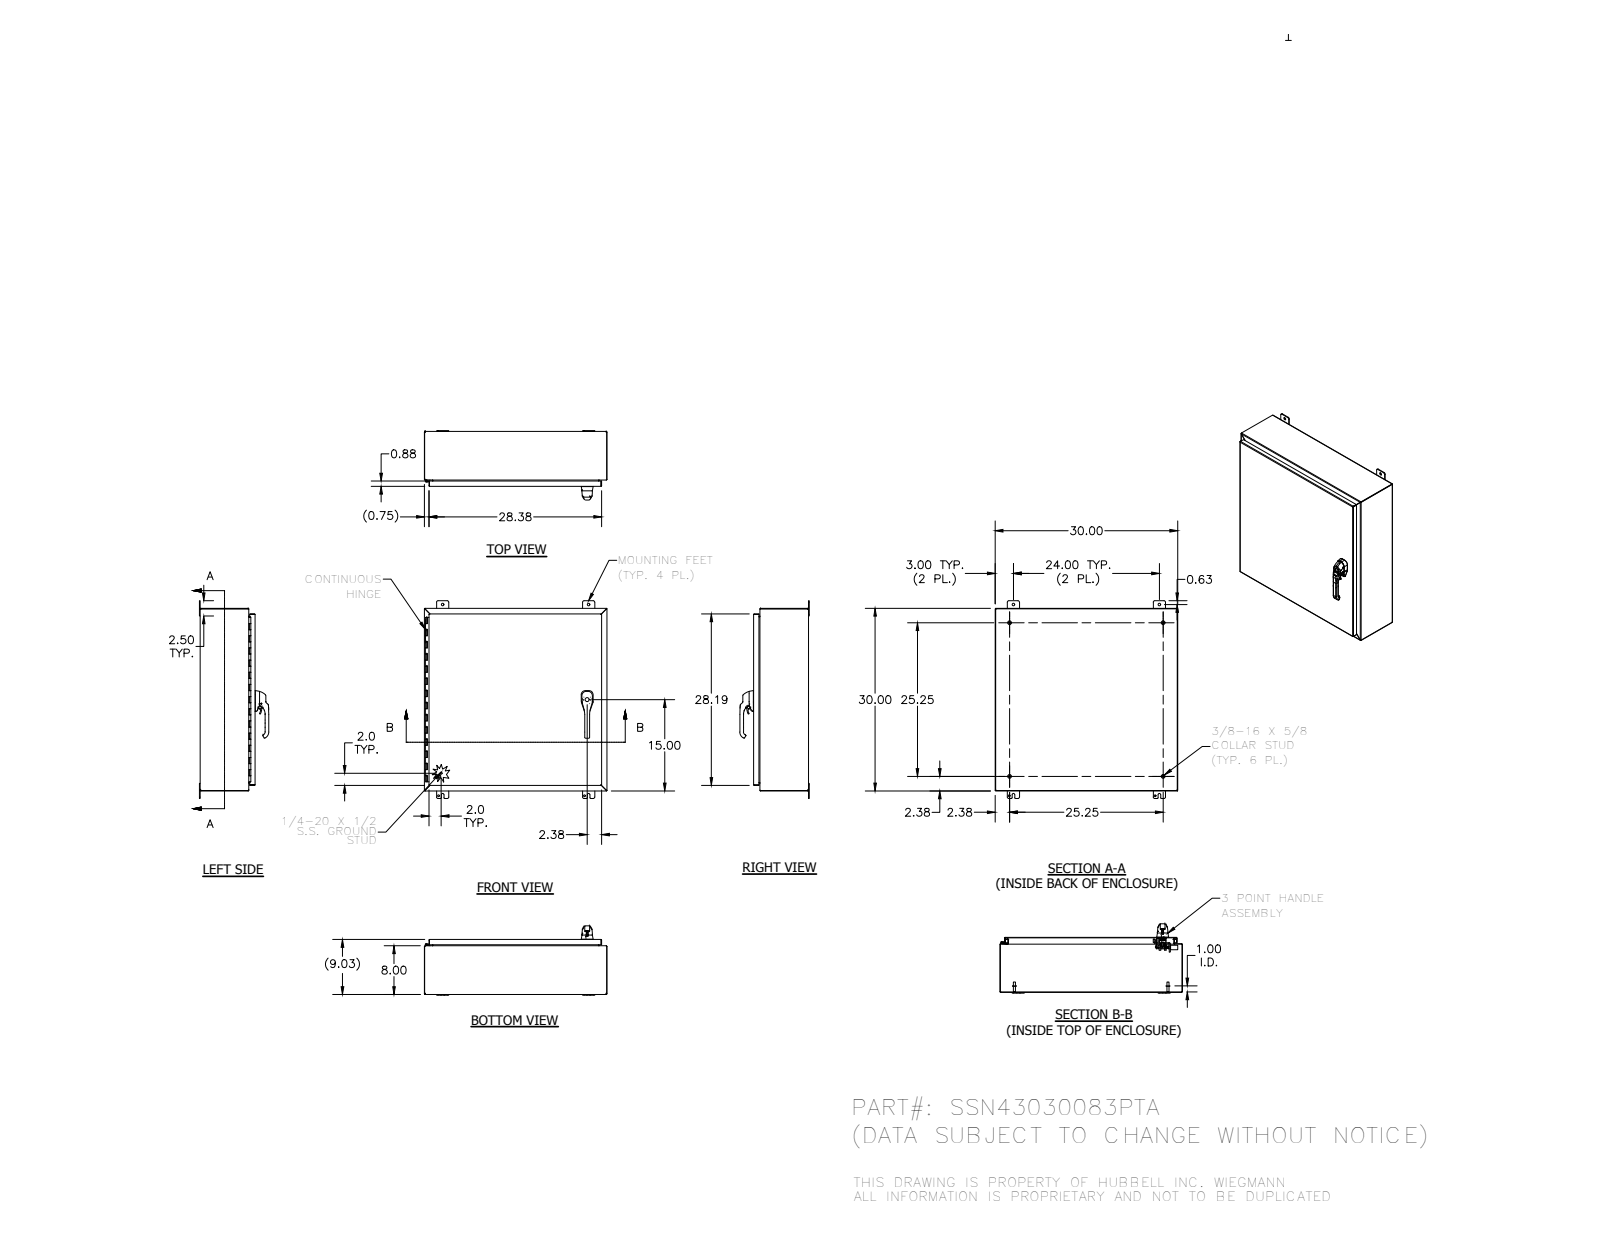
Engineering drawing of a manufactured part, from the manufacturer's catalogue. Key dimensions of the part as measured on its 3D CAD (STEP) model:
Part name (STEP PRODUCT): HFW32451; 1091-903_AF0; HFW3762; SSN43030083PTABKP (+8 more)
STEP written by: SolidWorks 2014 (AUTOMOTIVE_DESIGN)
Units: inches
Bodies: 56 solids, 3140 faces (1047 planar, 1306 cylindrical, 787 other)
Overall size (bounding box): 32.5 × 30 × 11.408
Volume: 254 in³ · Surface area: 6 591 in²
Round holes (diameter × count): ⌀0.262 ×8, ⌀0.187 ×4, ⌀0.313 ×4, ⌀0.438 ×4, ⌀0.213 ×3, ⌀0.281 ×3, ⌀0.241 ×2, ⌀0.25 ×2, ⌀0.252 ×2, ⌀0.315 ×2, ⌀0.4 ×2, ⌀0.402 ×2
Round bosses / shafts (diameter × count): ⌀0.625 ×4, ⌀0.33 ×4, ⌀0.236 ×3, ⌀1 ×2, ⌀0.563 ×2, ⌀0.533 ×2, ⌀0.531 ×2, ⌀0.5 ×2
Partial cylindrical surfaces — rounded edges, fillets, slot ends (radius × count): R0.02 ×172, R0.012 ×113, R0.125 ×26, R0.031 ×24, R0.019 ×21, R0.105 ×20, R0.25 ×20, R0.025 ×16
Main face-to-face distances: 0.074, 8.959, 29.926, 8.885, 9.033, 29.852, 30, 7.926, 1.033, 8
Hole centre spacings: 0.38, 0.492, 0.76, 24, 38.419, 0.886, 1.593, 20.428
